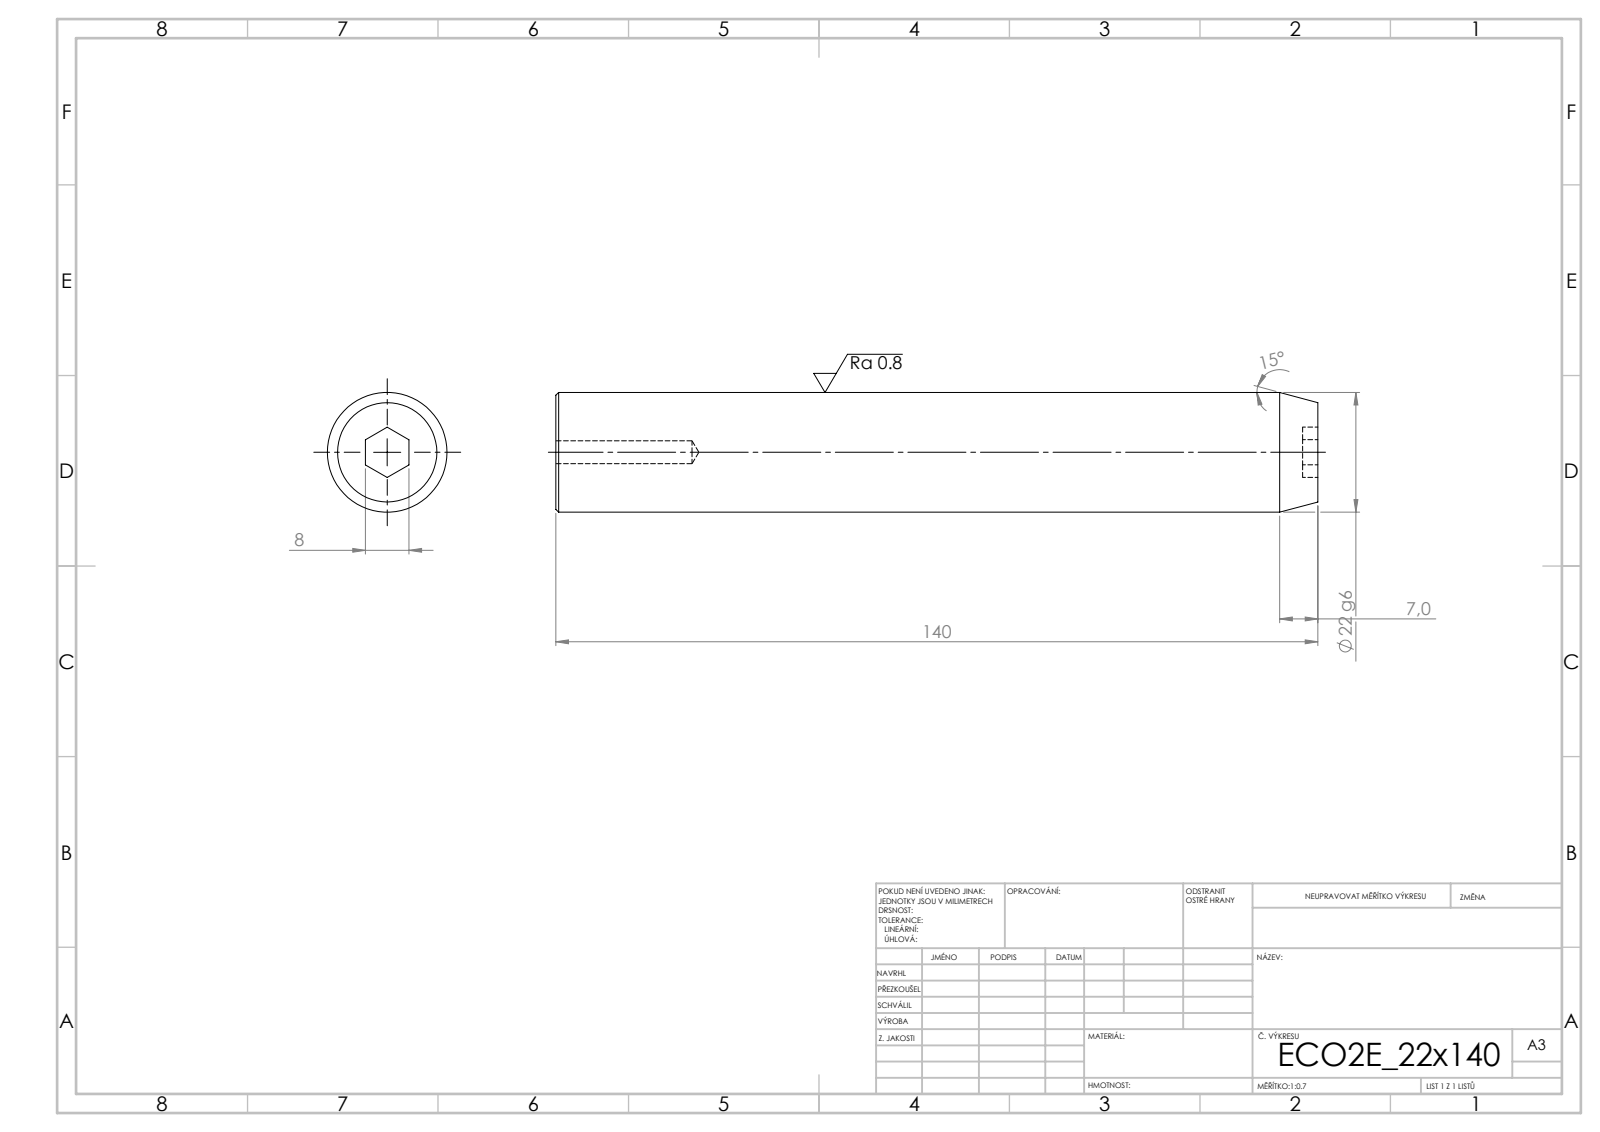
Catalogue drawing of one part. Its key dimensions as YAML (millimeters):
step_written_by: "SolidWorks 2019 (CONFIG_CONTROL_DESIGN)"
units: millimeters
bodies: {solids: 1, faces: 19, planar: 9, cylindrical: 4, other: 6}
overall_size: [140, 22, 22]
volume: 52275
surface_area: 10681
round_holes:
  - {diameter: 4.2, count: 1}
round_bosses_or_shafts:
  - {diameter: 22, count: 1}
face_to_face_distances: [140, 2.8, 137.2, 8]
